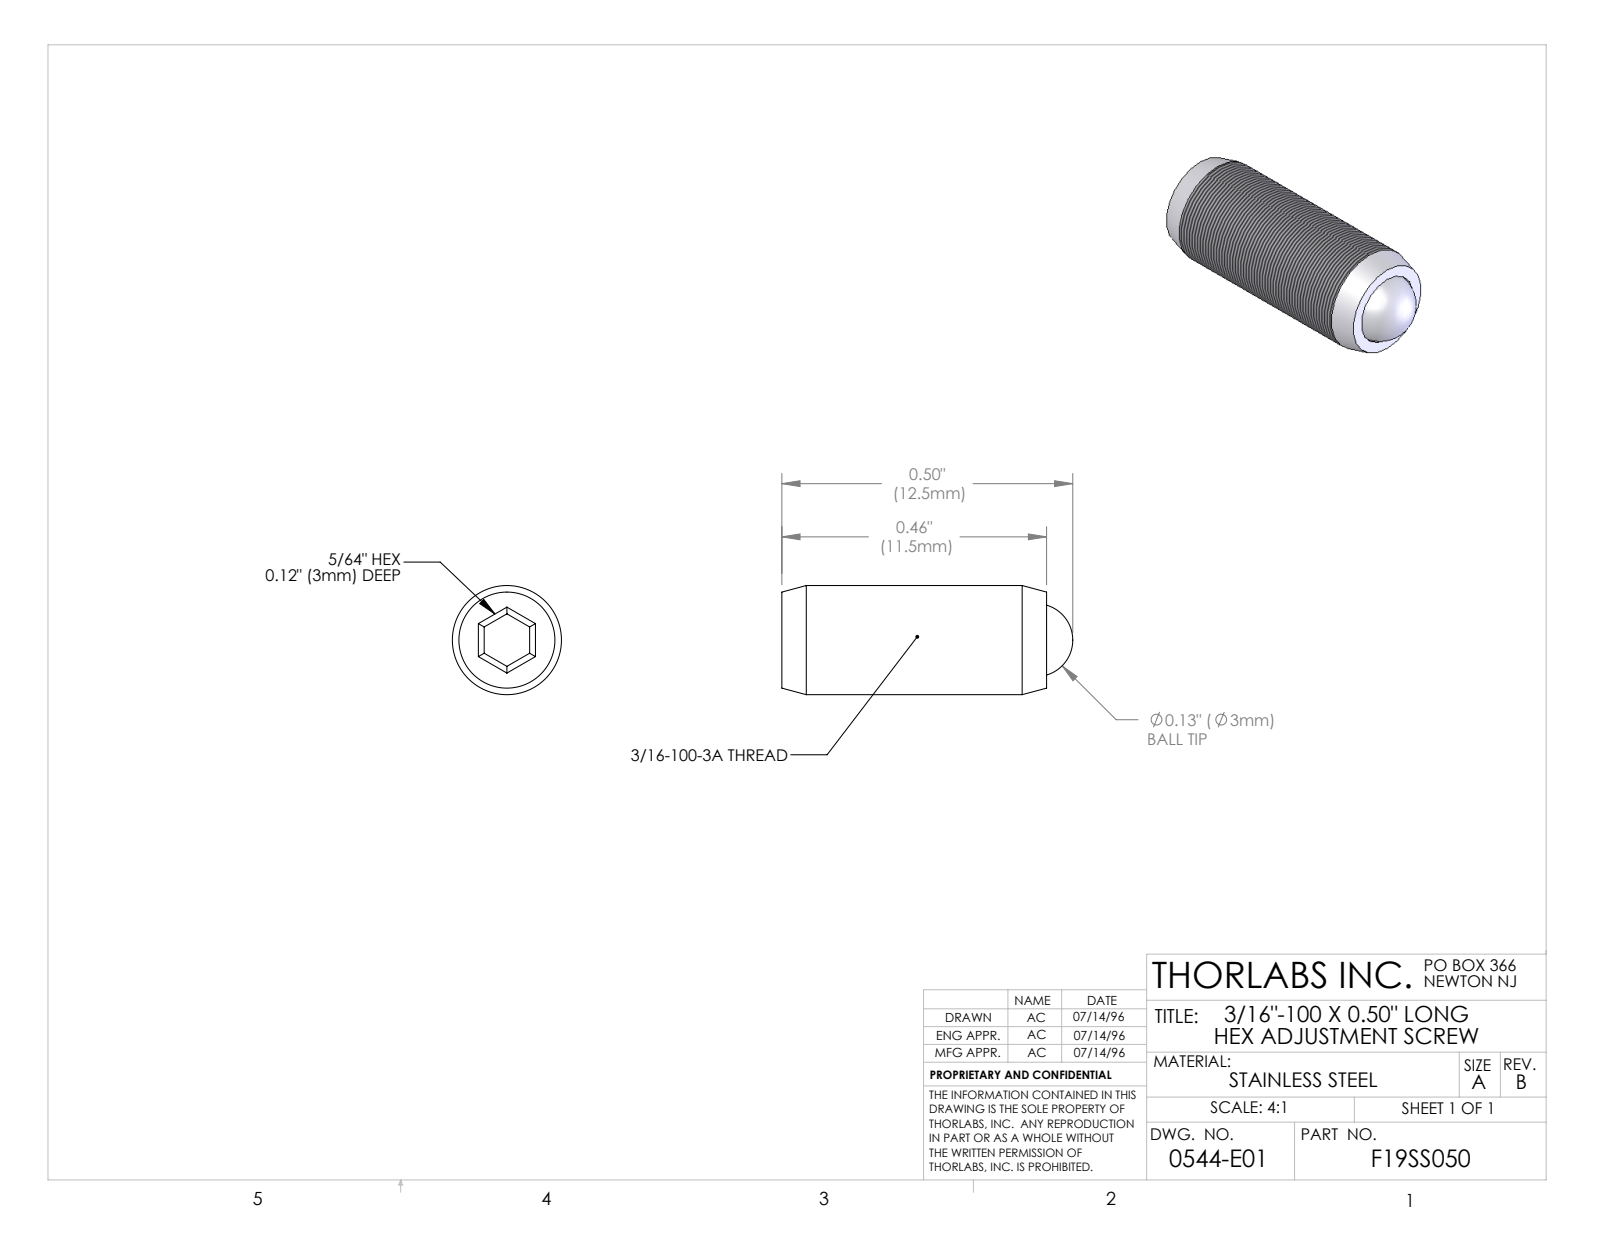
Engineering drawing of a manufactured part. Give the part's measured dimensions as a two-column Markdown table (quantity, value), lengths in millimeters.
| quantity | value |
| --- | --- |
| part name | 0544-E0W |
| STEP written by | SolidWorks 2007 (AUTOMOTIVE_DESIGN) |
| units | millimeters |
| bodies | 2 solids, 29 faces (15 planar, 4 cylindrical, 10 other) |
| overall size | 12.7 × 4.76 × 4.76 |
| volume | 195 mm³ |
| surface area | 266 mm² |
| round holes (diameter × count) | 3.19 × 1 |
| round bosses / shafts (diameter × count) | 4.76 × 1 |
| main face-to-face distances | 1.98, 11.56, 3.05, 8.51, 1.99 |
